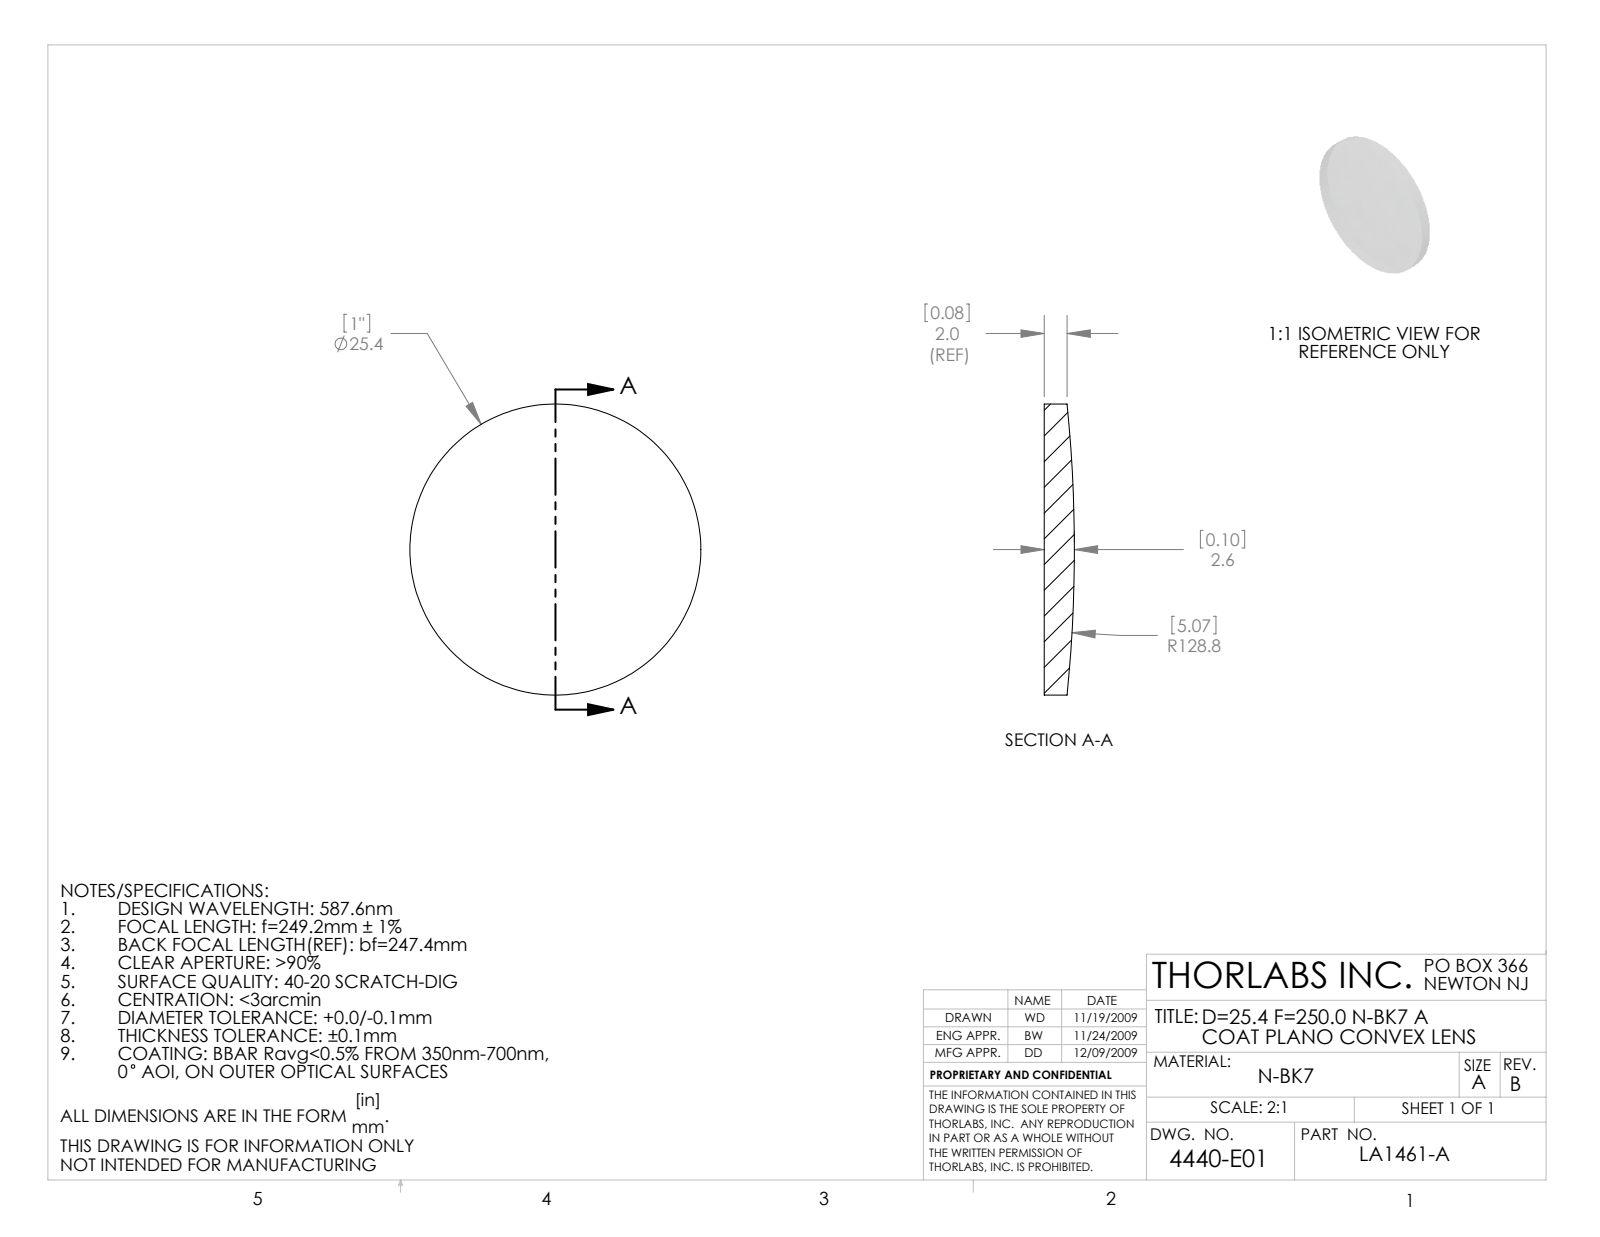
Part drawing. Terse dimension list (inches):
name: 4440-E0W
written by: SolidWorks 2009 (AUTOMOTIVE_DESIGN)
unit: in
bodies: 1 solid, 5 faces (1 planar, 2 cylindrical, 2 other)
size: 1 × 1 × 0.103
volume: 0.071 in³; area: 1.82 in²
bosses: 1× ⌀1
